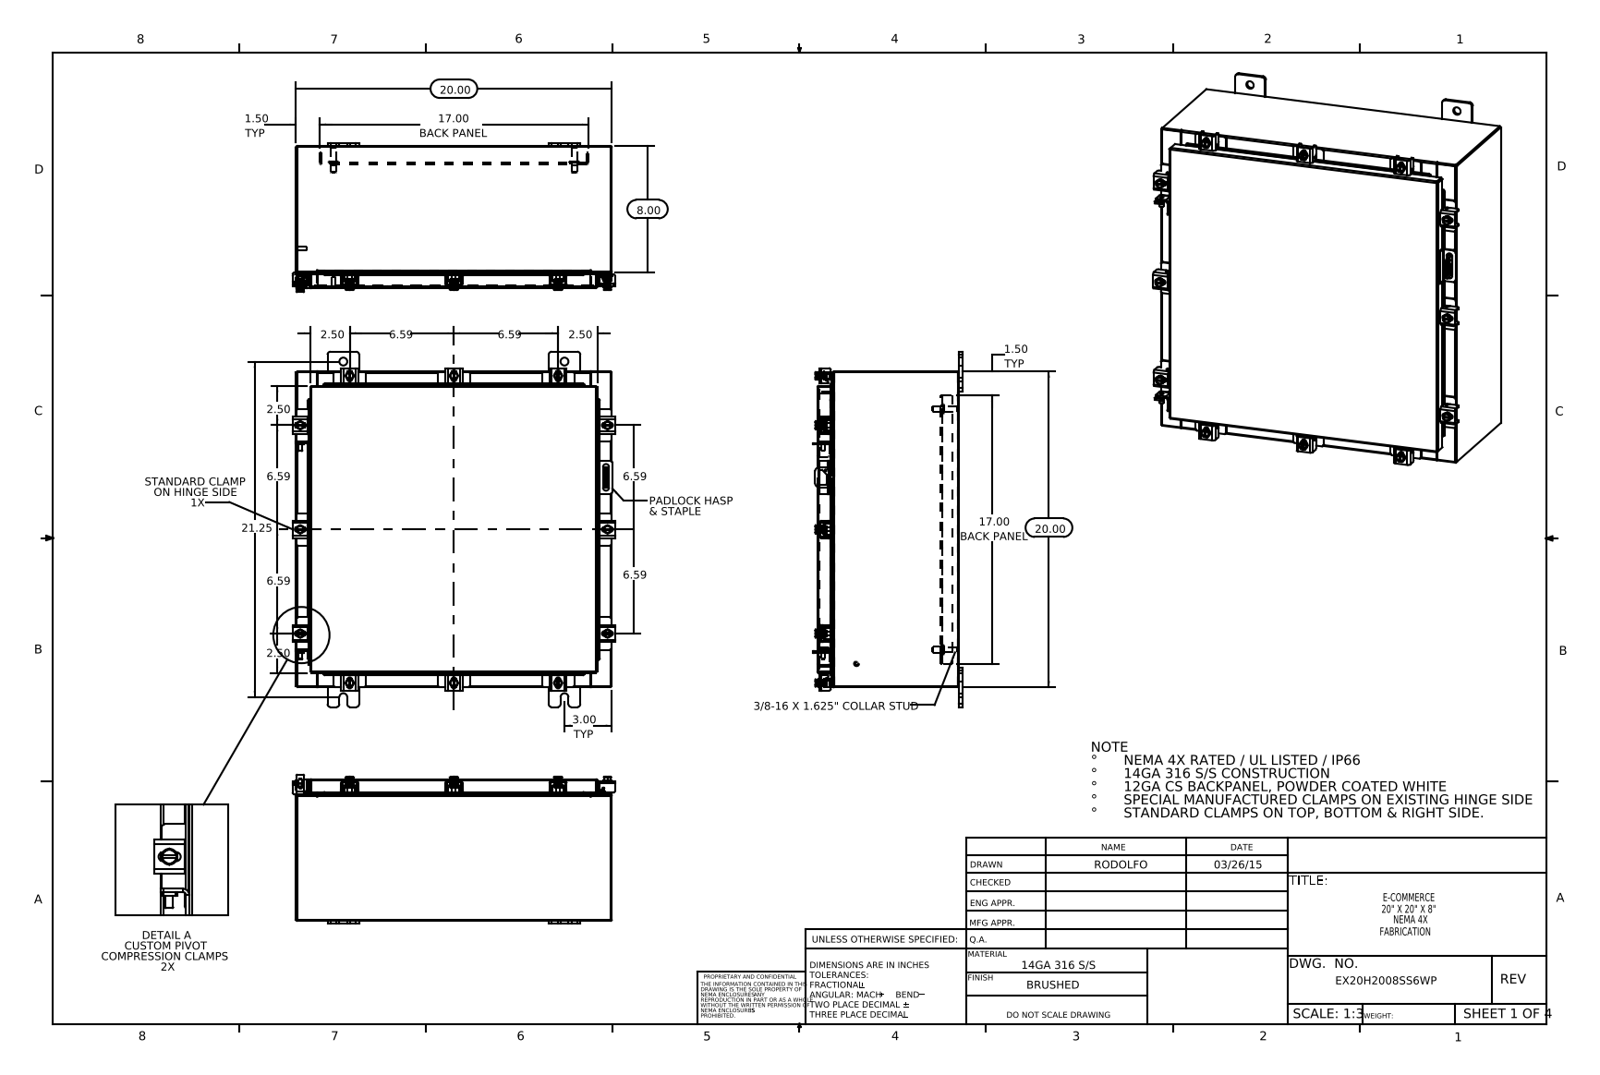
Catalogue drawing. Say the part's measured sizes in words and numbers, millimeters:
The part is named "Quarter-20 CD Stud; 30X10 Clamp Bracket2; EX20H2008SS6WP; EX20H2008SS6WP Mounting Studs (+8 more)". Its 3-D file was written by "SolidWorks 2014 (CONFIG_CONTROL_DESIGN)". It is 81 solids with 2018 faces: 1075 planar, 783 cylindrical and 160 other. Overall it measures 571.5 by 518.7 by 240.1 millimeters. Its volume is 2 648 000 cubic millimeters and its surface area 2 615 000 square millimeters. Round holes: 12 of diameter 5.4, 12 of diameter 6.6, 8 of diameter 12.7, 1 of diameter 3.2, 1 of diameter 6.4. Round bosses or shafts: 12 of diameter 12.7, 12 of diameter 6.4, 10 of diameter 10.1, 4 of diameter 15.9, 4 of diameter 9.5, 4 of diameter 8.4, 2 of diameter 8, 2 of diameter 6. Partial cylindrical surfaces (rounded edges, fillets, slot ends): 54 of radius 1.5, 24 of radius 0.3, 24 of radius 3.6, 24 of radius 4.8, 22 of radius 2.2, 22 of radius 3, 18 of radius 2.3, 17 of radius 1.3. The main face-to-face distances are 1.9, 226.1, 506.1, 228, 224.2, 504.2, 508, 2.6, 25.4, 27.3. The hole center spacings are 167.5, 259.5, 422.1, 482.5, 521.7, 59.4, 365.1, 441.5.
